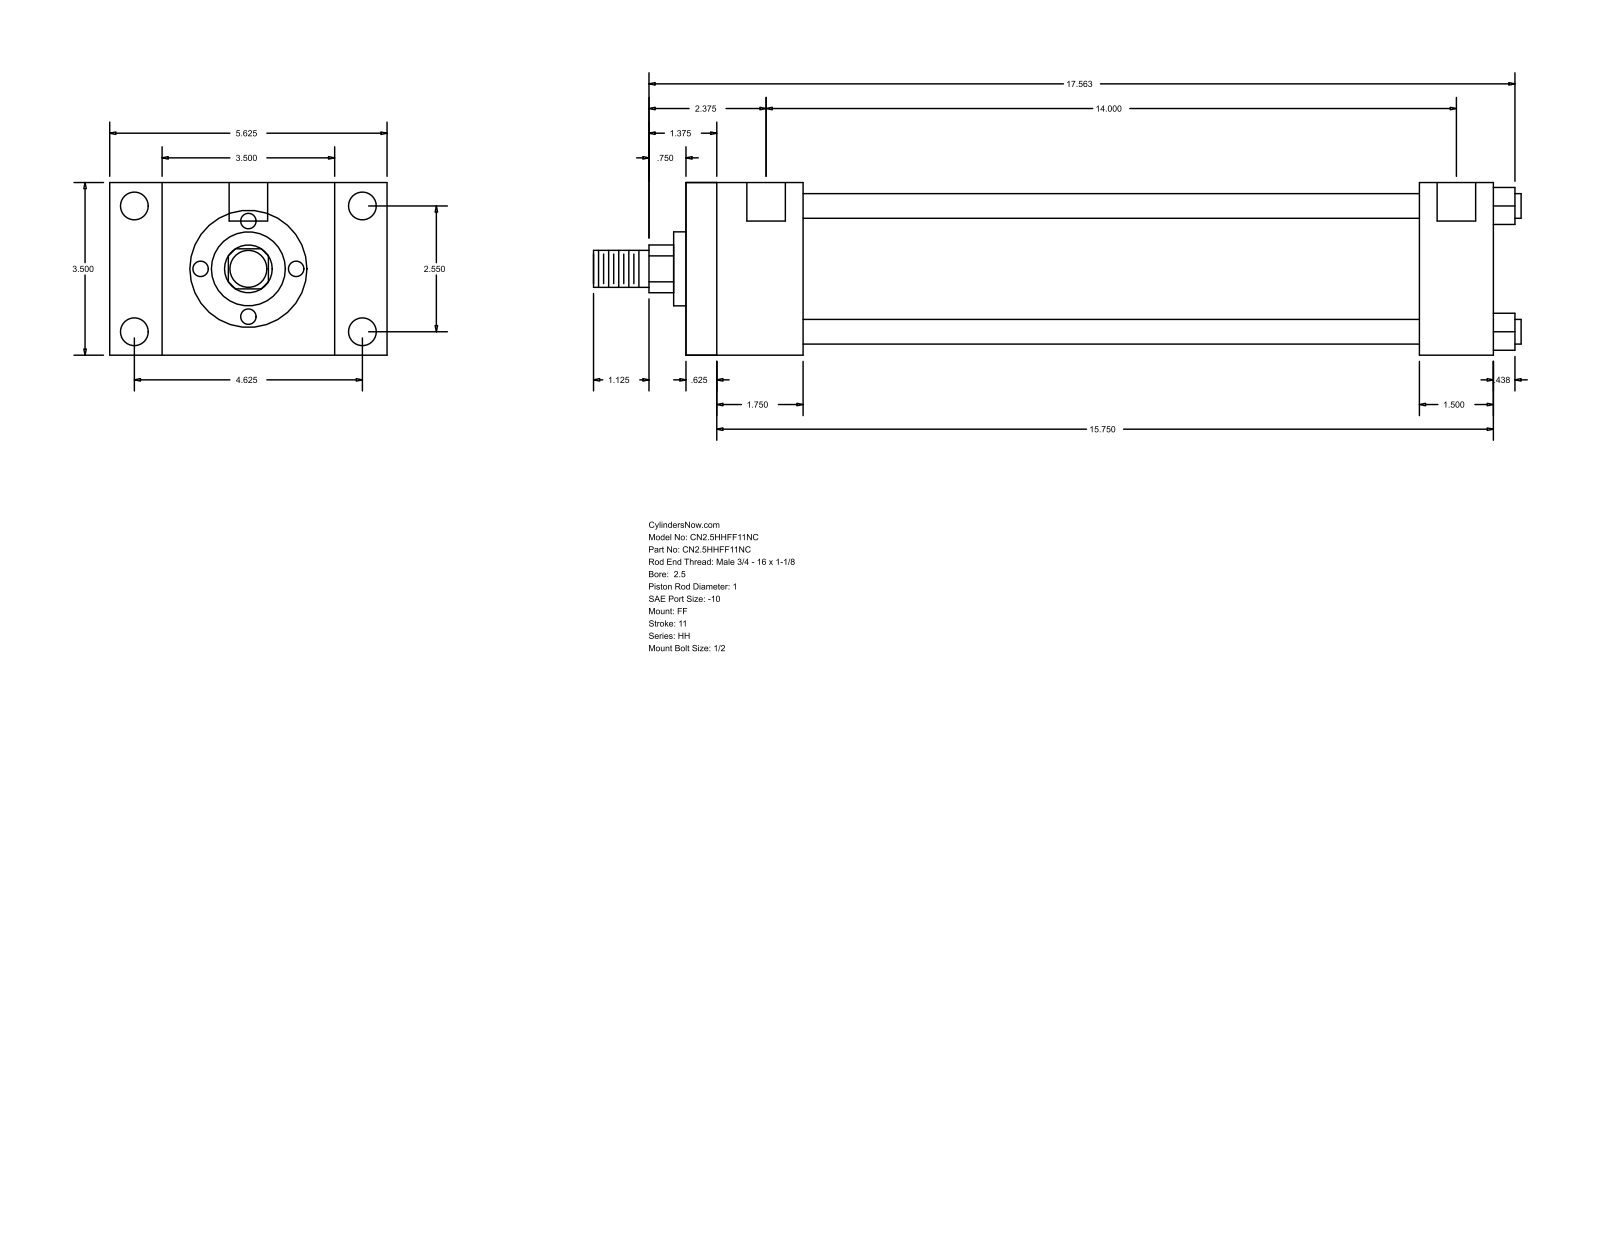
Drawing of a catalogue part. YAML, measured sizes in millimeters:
part_name: "HH_FF__0250_1"
step_written_by: "GSSL Pune (CONFIG_CONTROL_DESIGN)"
units: millimeters
bodies: {solids: 0, faces: 92, planar: 64, cylindrical: 28, other: 0}
overall_size: [477.84, 142.88, 88.9]
round_holes:
  - {diameter: 5.56, count: 4}
  - {diameter: 14.3, count: 4}
  - {diameter: 19.84, count: 2}
round_bosses_or_shafts:
  - {diameter: 12.7, count: 4}
  - {diameter: 73.03, count: 1}
  - {diameter: 38.1, count: 1}
  - {diameter: 25.4, count: 1}
  - {diameter: 19.05, count: 1}
partial_cylinders:
  - {radius: 12.29, count: 1}
face_to_face_distances: [88.9, 415.93, 15.87, 400.06, 38.1, 60.33, 44.46, 355.6, 377.83, 361.96]
hole_center_spacings: [64.76, 117.48, 134.15, 358.77, 1.58, 1.59, 355.6, 357.18]
